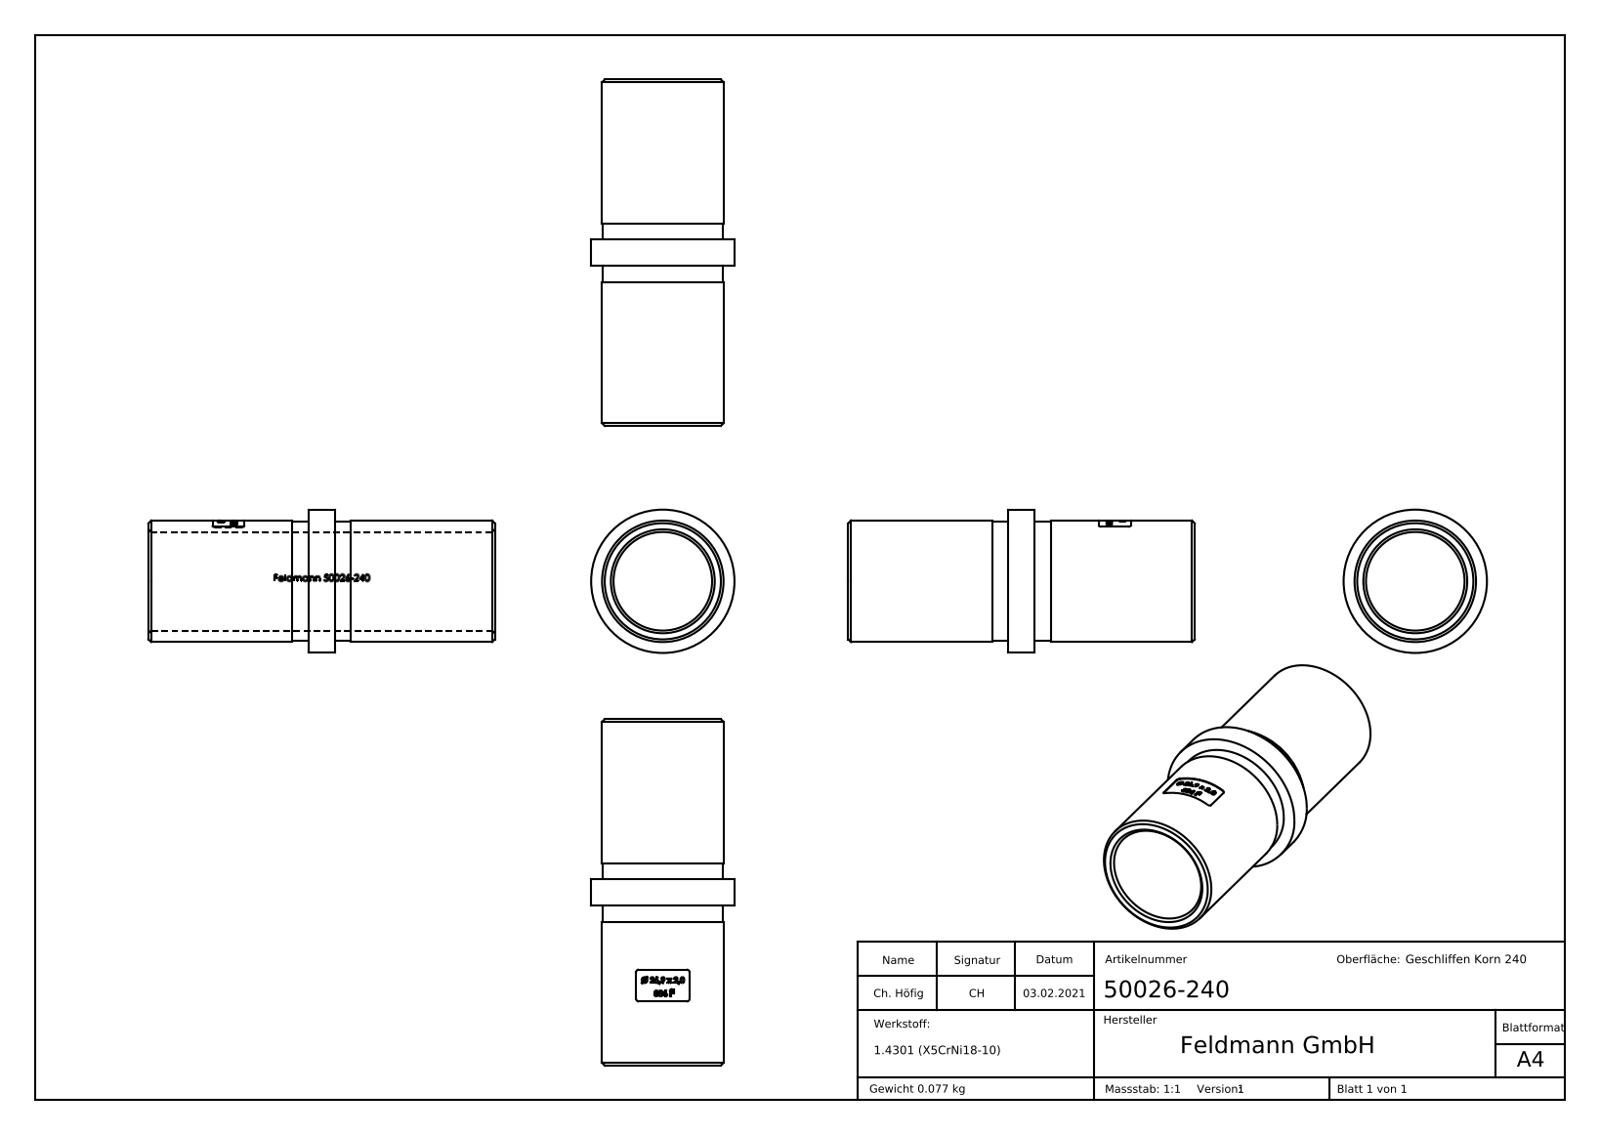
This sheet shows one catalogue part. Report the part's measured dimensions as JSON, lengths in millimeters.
{"part_name": "50026-240", "step_written_by": "SolidWorks 2018 (CONFIG_CONTROL_DESIGN)", "units": "millimeters", "bodies": {"solids": 1, "faces": 416, "planar": 177, "cylindrical": 56, "other": 183}, "overall_size": [65, 26.9, 26.9], "volume_mm3": 9741, "surface_area_mm2": 9089, "round_holes": [[18.5, 1]], "round_bosses_or_shafts": [[26.9, 1], [22.8, 1], [22.4, 1]], "partial_cylinders_radius": [[0.5, 4], [9.35, 1], [11.3, 1]], "face_to_face_distances": [5, 30, 35, 65, 27, 38, 3, 8, 11, 12]}
